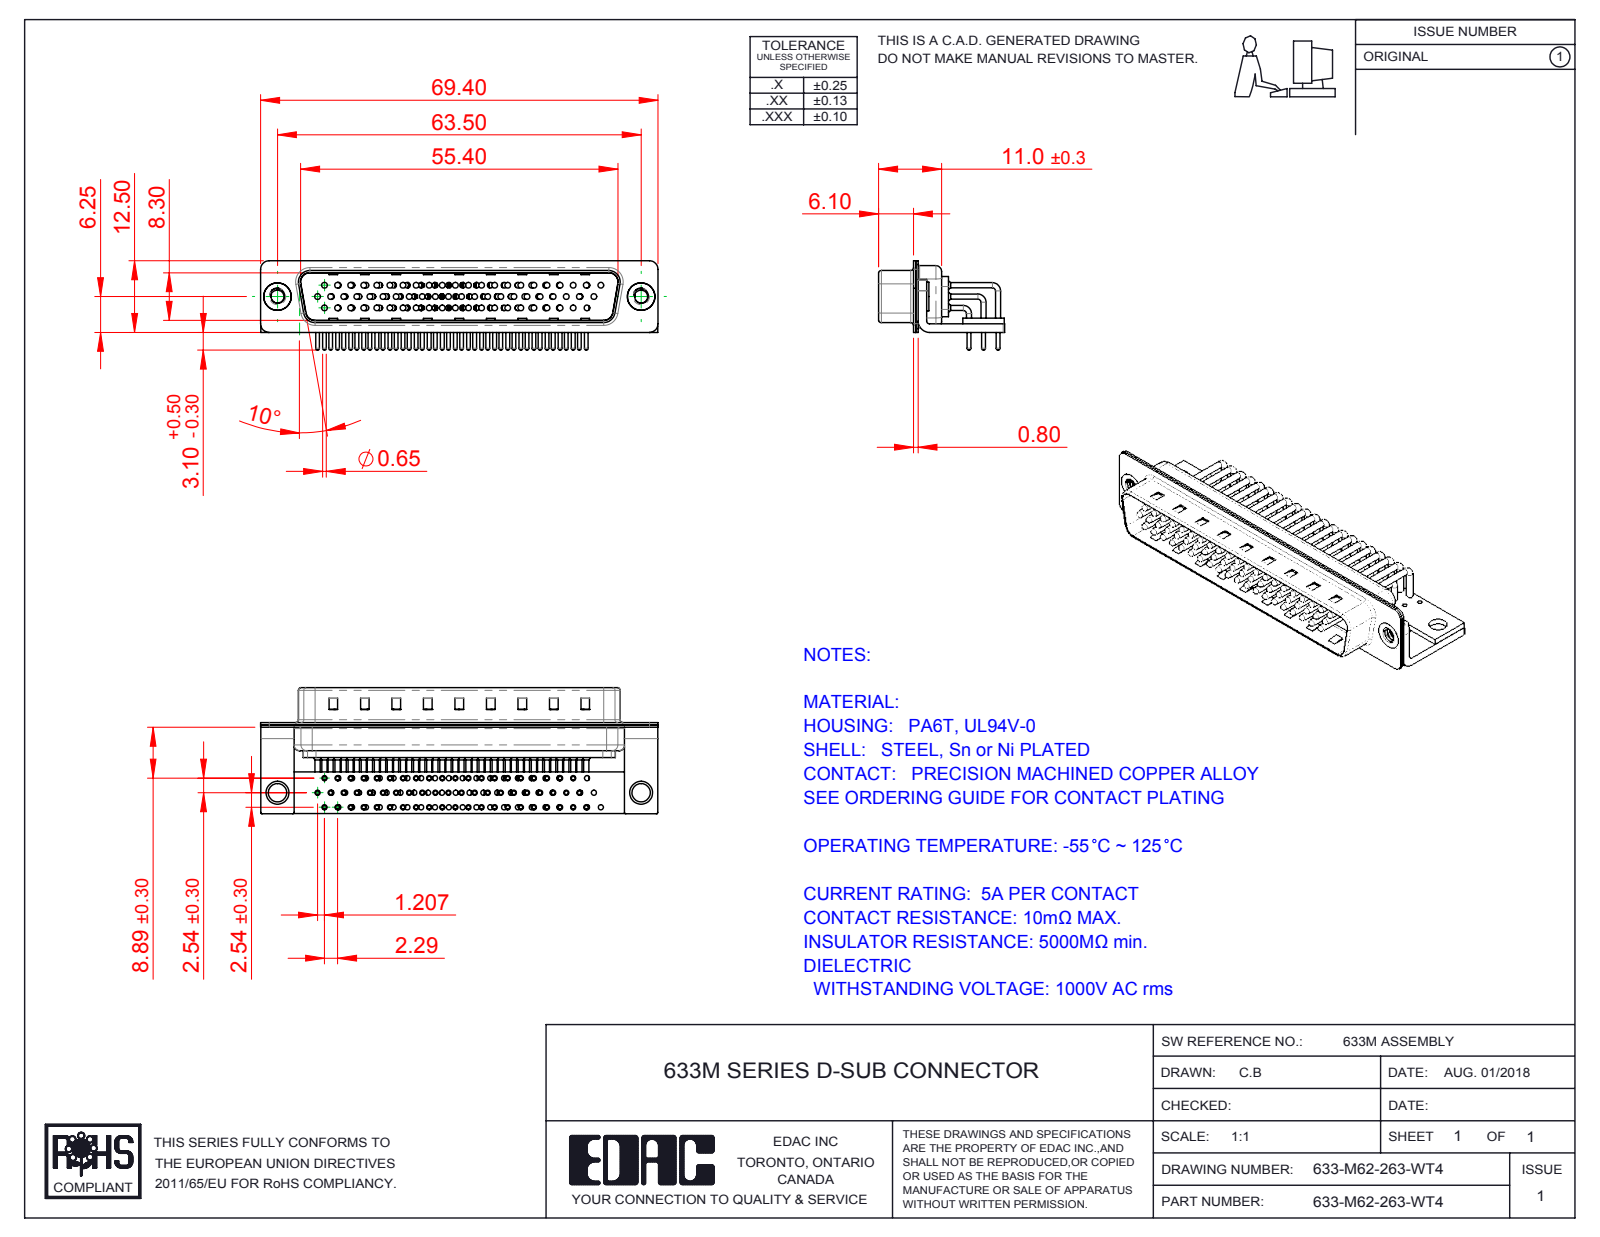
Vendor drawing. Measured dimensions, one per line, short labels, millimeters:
name: 633M Contact Row 2; 633M 4-40 Threaded Rivet_Stabilizer; 633M Stabilizer Bracket; 633M Shell Front_62 Contacts (+6 more)
written by: SolidWorks 2016 (CONFIG_CONTROL_DESIGN)
unit: mm
bodies: 70 solids, 7406 faces (4197 planar, 2519 cylindrical, 690 other)
size: 69.4 × 22 × 15.6
volume: 5 073 mm³; area: 15 493 mm²
holes: 62× ⌀0.9, 62× ⌀1, 62× ⌀1.7, 62× ⌀2, 2× ⌀2.26, 2× ⌀3.2, 2× ⌀4, 2× ⌀4.8
bosses: 118× ⌀0.9, 62× ⌀1.5, 62× ⌀0.65, 56× ⌀1, 2× ⌀5, 2× ⌀4.9
rounds: 62× R1.01, 16× R0.25, 16× R1.5, 13× R2, 9× R0.5, 8× R1.6, 4× R0.6, 4× R0.65
face distances: 0.4, 0.85, 1.25, 1.5, 9.55, 1, 1.9, 10.4, 0.8, 8.3
hole spacings: 7.24, 2.41, 9.65, 4.83, 14.48, 16.89, 2.81, 2.32
